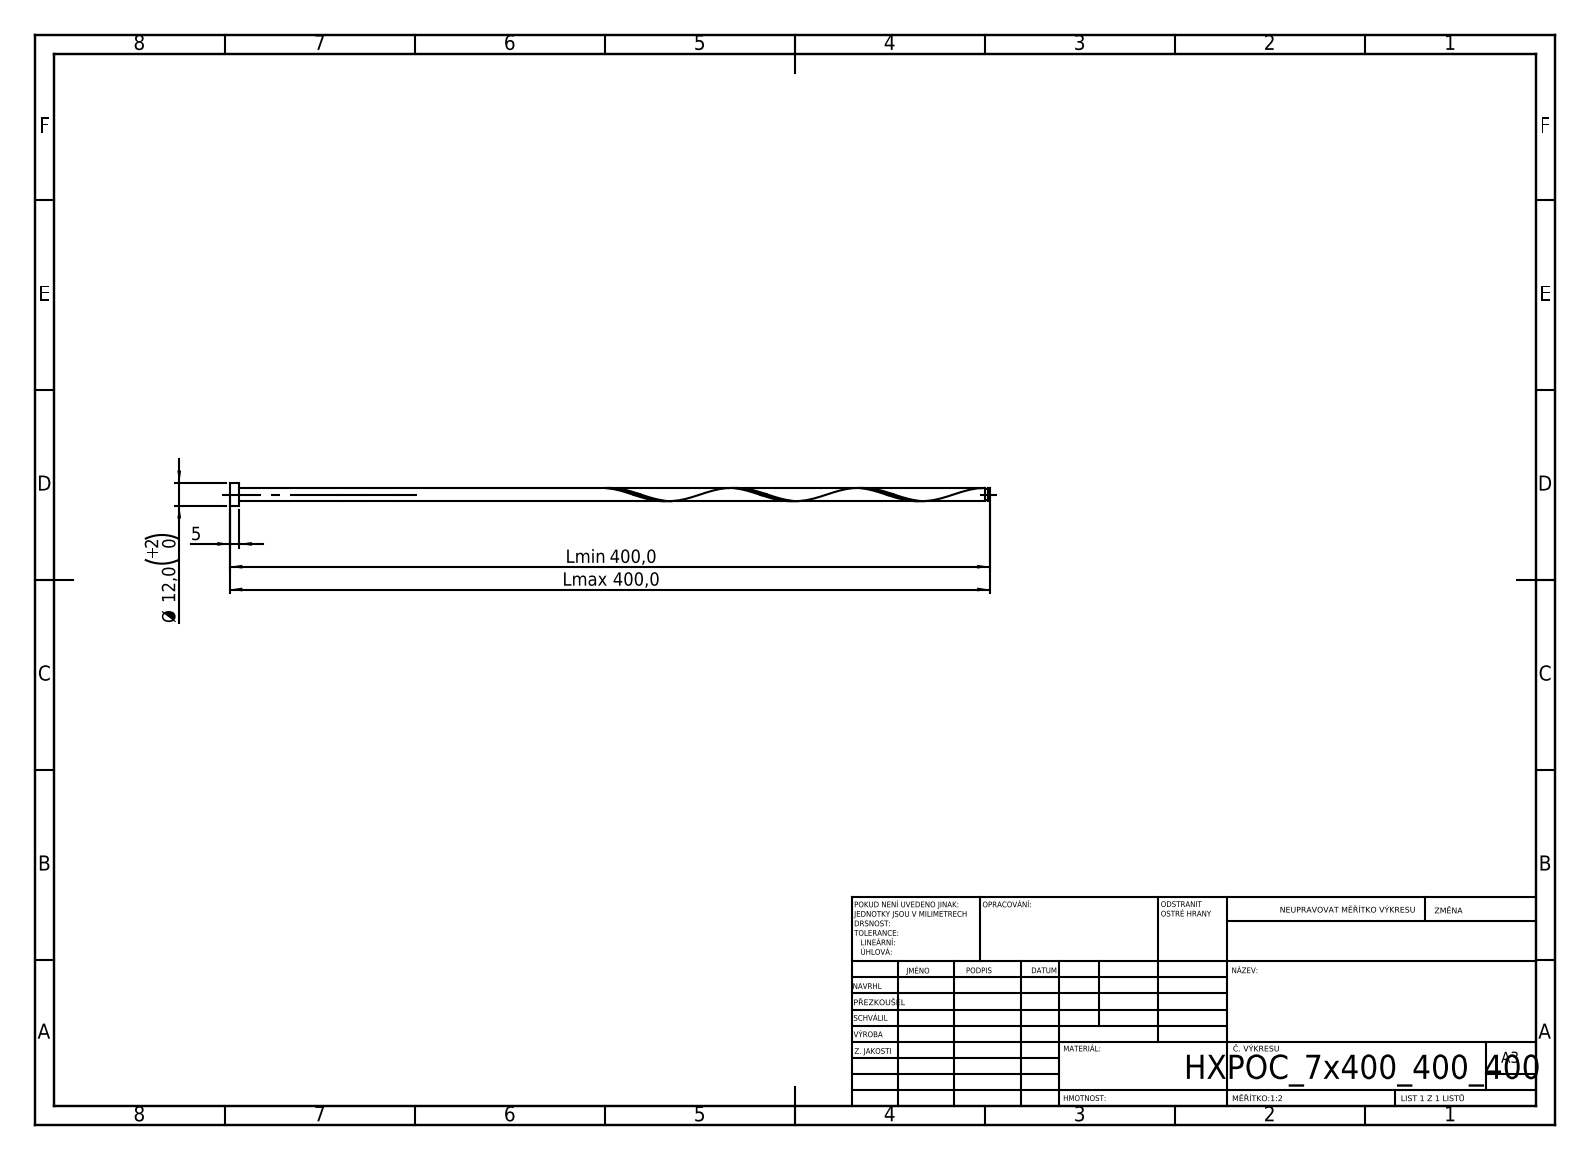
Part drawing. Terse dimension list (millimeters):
written by: SolidWorks 2019 (CONFIG_CONTROL_DESIGN)
unit: mm
bodies: 1 solid, 16 faces (6 planar, 9 cylindrical, 1 other)
size: 400 × 12 × 12
volume: 19 023 mm³; area: 12 198 mm²
bosses: 1× ⌀12, 1× ⌀7, 1× ⌀5.6
face distances: 5, 400, 395, 399, 394, 1, 397.6, 392.6, 1.4, 2.4
